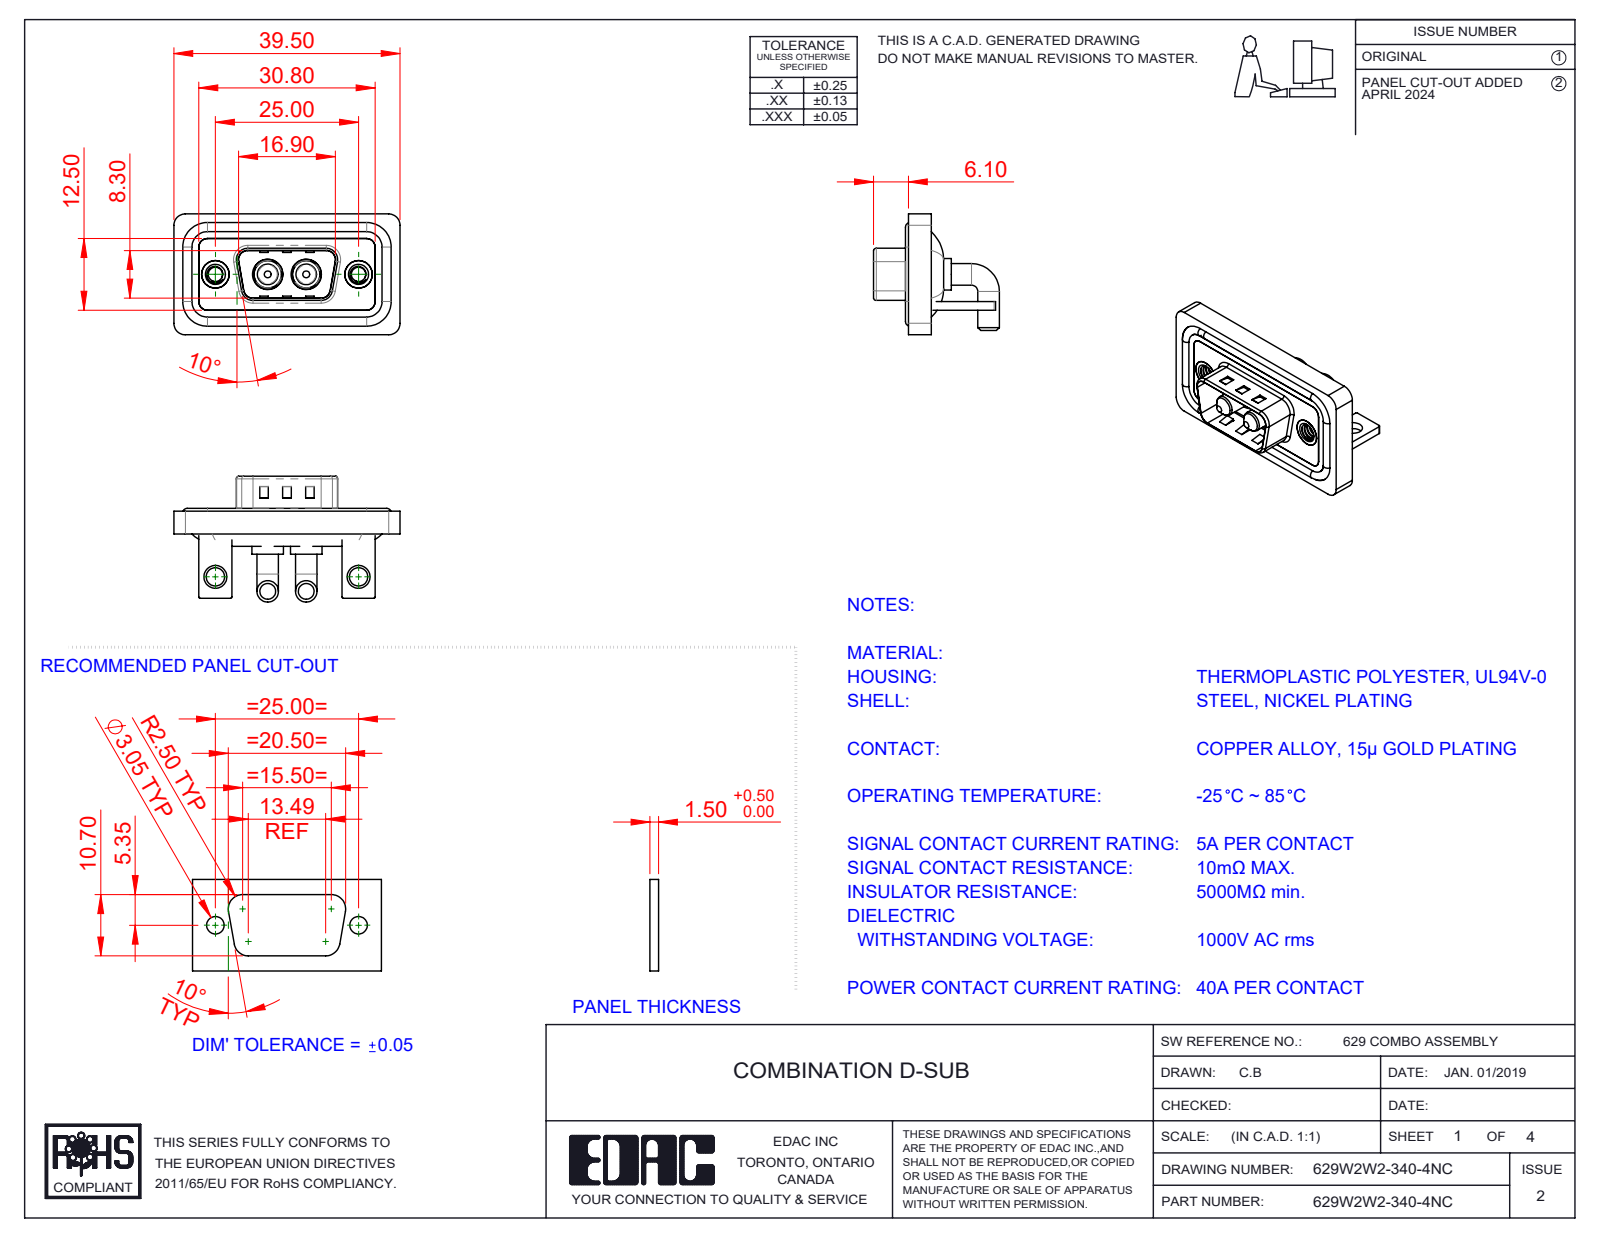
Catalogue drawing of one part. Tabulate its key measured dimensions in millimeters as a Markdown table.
| quantity | value |
| --- | --- |
| part name | 629Combo Stabilizer Bracket; Power Pin_40A RA; 629W2W2-340-4NC; 629Combo Shell Rear_09 Contacts (+4 more) |
| STEP written by | SolidWorks 2023 (CONFIG_CONTROL_DESIGN) |
| units | millimeters |
| bodies | 13 solids, 535 faces (185 planar, 240 cylindrical, 110 other) |
| overall size | 39.5 × 21.98 × 21.1 |
| volume | 5 002 mm³ |
| surface area | 7 843 mm² |
| round holes (diameter × count) | 2.5 × 2, 3.2 × 2, 4 × 2, 4.8 × 2, 4.85 × 2, 5 × 2, 5.3 × 2 |
| round bosses / shafts (diameter × count) | 3.75 × 4, 1.6 × 4, 5.5 × 2, 5.2 × 2, 4.9 × 2, 4.75 × 2, 3.6 × 2 |
| partial cylindrical surfaces (radius × count) | 2 × 19, 1.5 × 18, 0.25 × 16, 0.5 × 9, 1.6 × 8, 0.6 × 4, 0.65 × 4, 0.9 × 4 |
| main face-to-face distances | 0.4, 1.5, 2.9, 0.8, 1.1, 1.2, 2.1, 1.6, 3.7, 2.5 |
| hole center spacings | 9.14, 15.86, 25, 6.72 |
